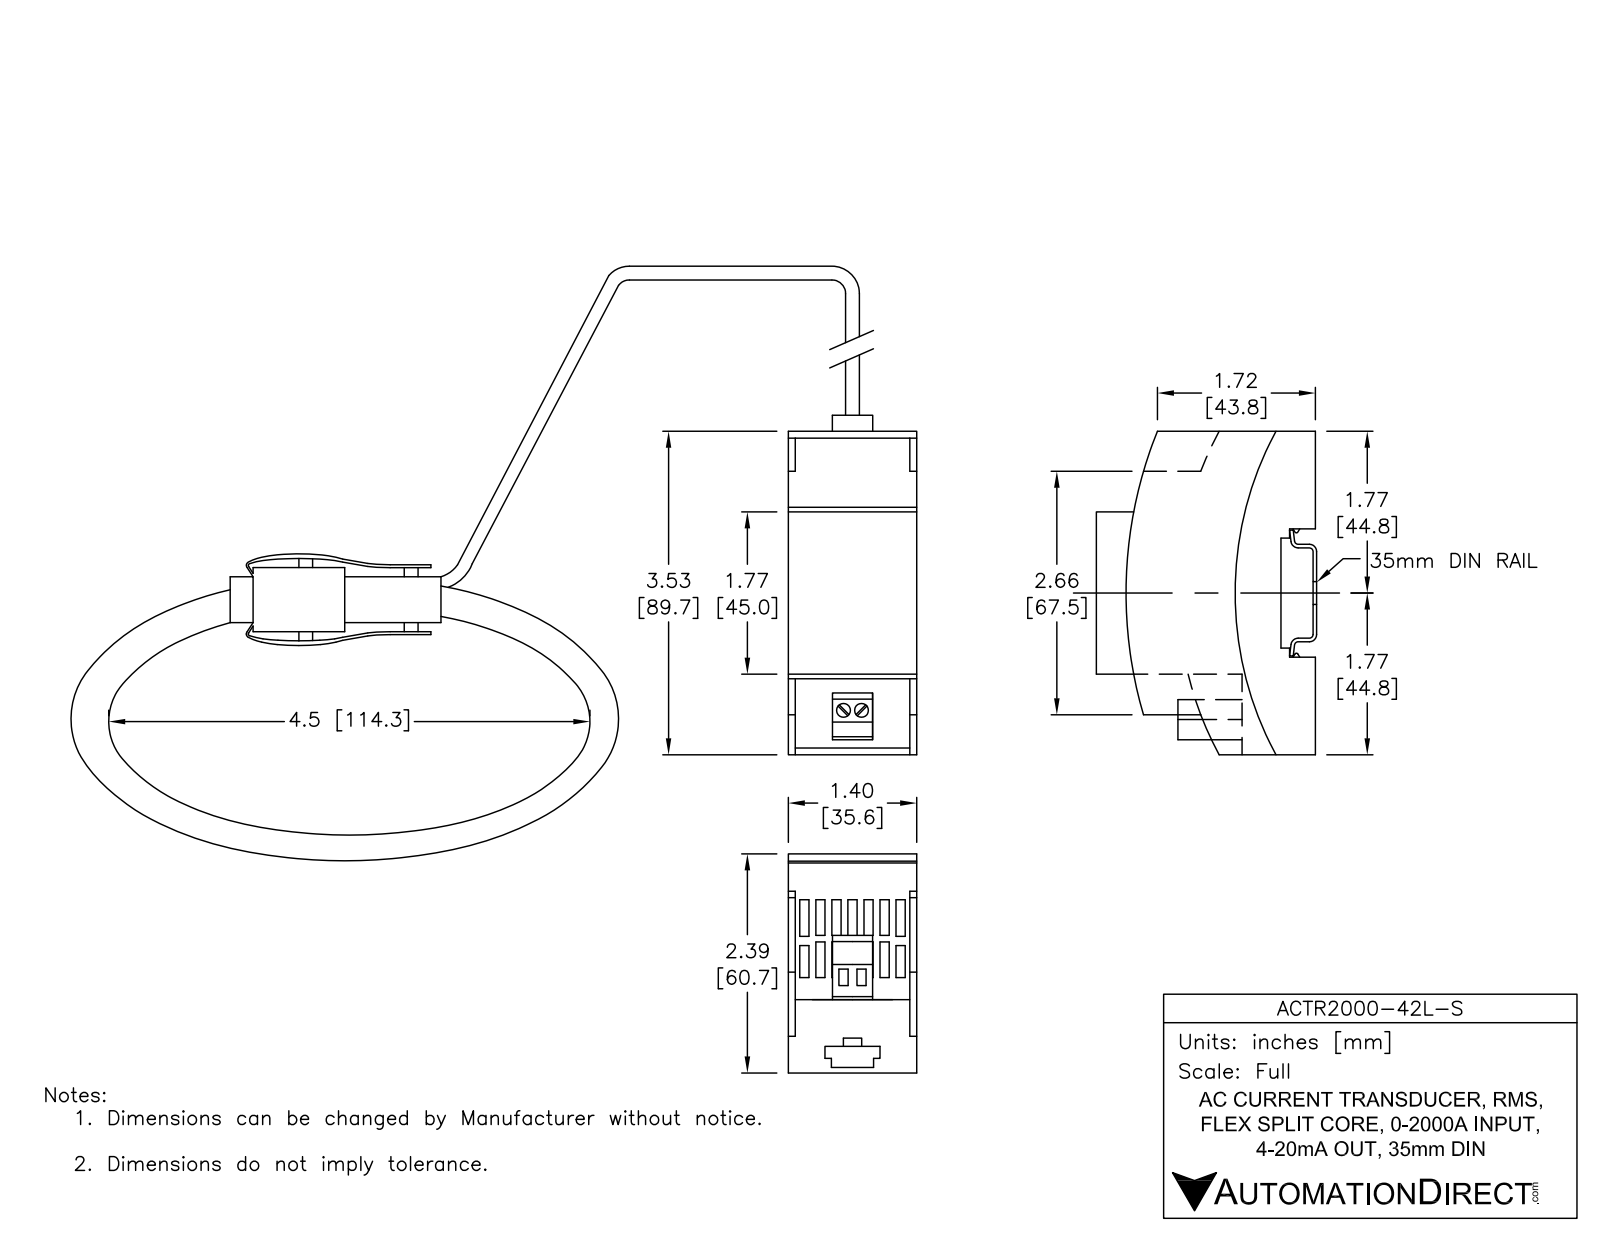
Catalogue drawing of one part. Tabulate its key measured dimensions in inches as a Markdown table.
| quantity | value |
| --- | --- |
| part name | ACTR2000-42L-S |
| STEP written by | SolidWorks 2021 (AUTOMOTIVE_DESIGN) |
| units | inches |
| bodies | 8 solids, 723 faces (379 planar, 123 cylindrical, 221 other) |
| overall size | 4.203 × 2.298 × 1.46 |
| volume | 3.122 in³ |
| surface area | 82.28 in² |
| round holes (diameter × count) | 0.157 × 2 |
| round bosses / shafts (diameter × count) | 0.15 × 2, 0.543 × 1, 0.018 × 1 |
| partial cylindrical surfaces (radius × count) | 0.02 × 22, 0.006 × 10, 0.01 × 10, 0.02 × 10, 0.039 × 10, 0.026 × 8, 0.008 × 4, 0.032 × 4 |
| main face-to-face distances | 1.435, 0.064, 0.436, 0.5, 0.059, 1.267, 1.261, 0.266, 0.702, 0.766 |
| hole center spacings | 0.2 |
